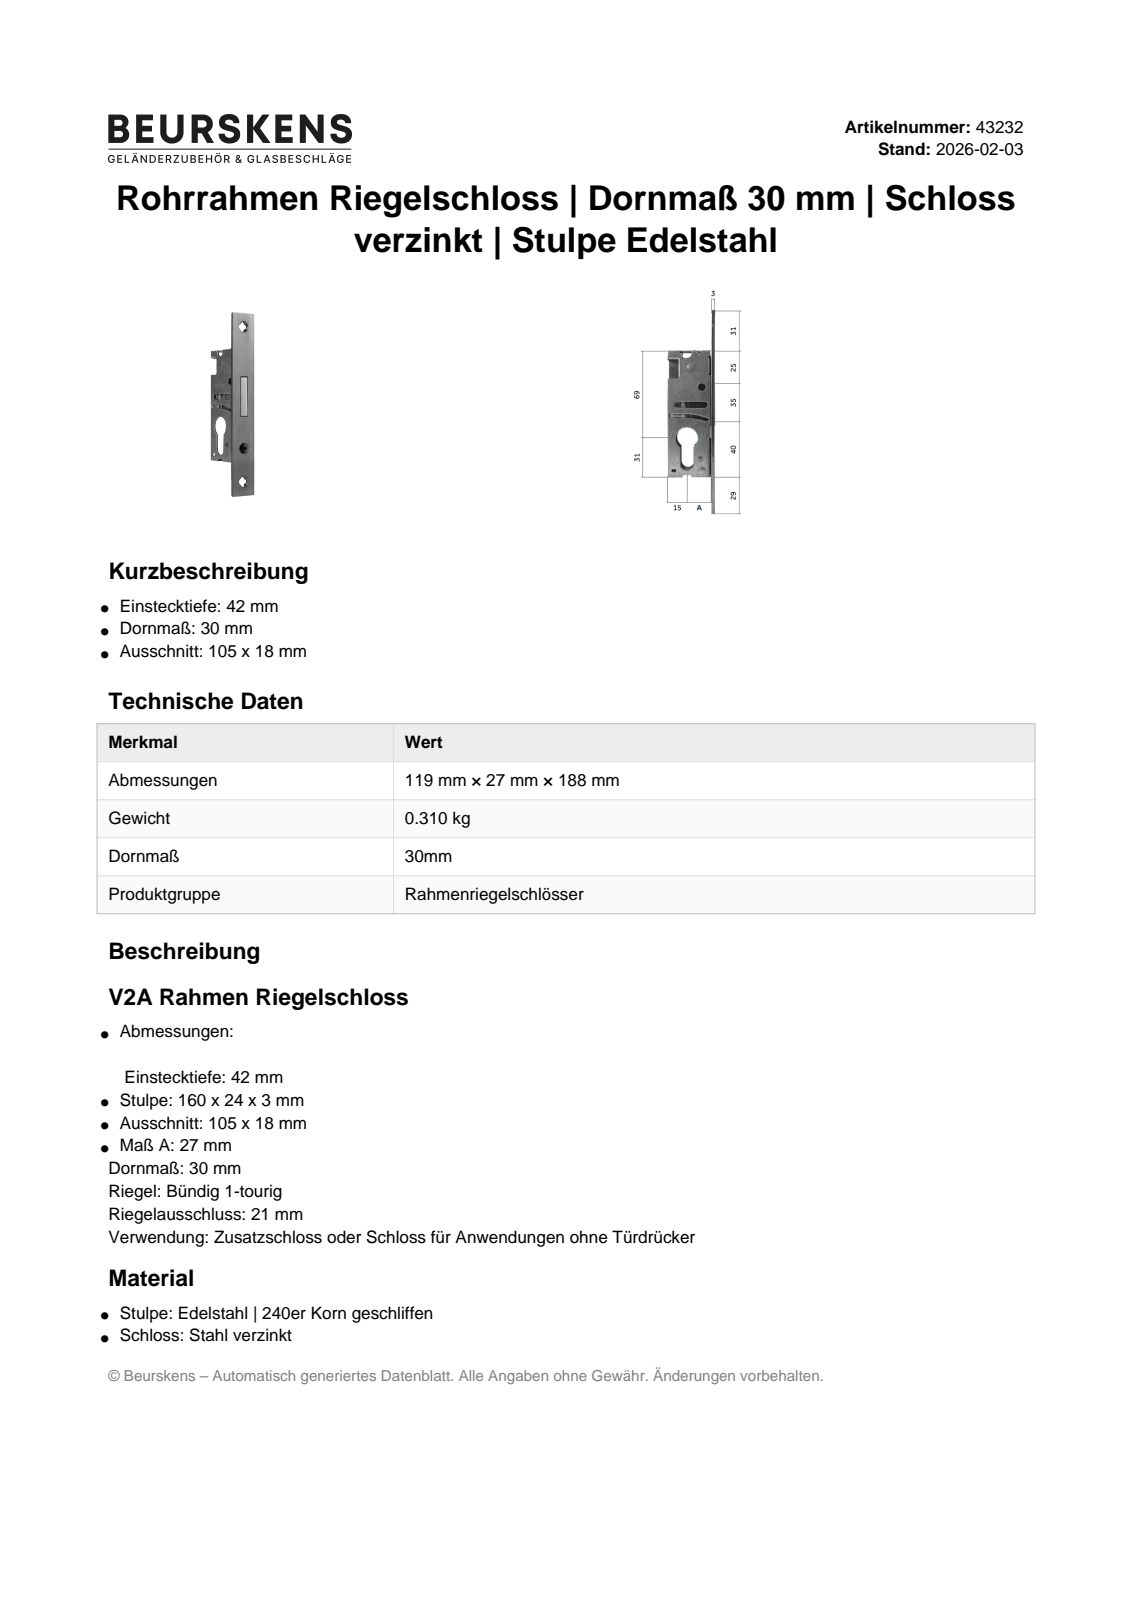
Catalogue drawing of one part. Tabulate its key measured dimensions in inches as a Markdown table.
| quantity | value |
| --- | --- |
| part name | 43232 |
| STEP written by | Autodesk Inventor 2022 (AUTOMOTIVE_DESIGN) |
| units | inches |
| bodies | 1 solid, 26 faces (18 planar, 5 cylindrical, 3 other) |
| overall size | 6.299 × 2.598 × 0.945 |
| volume | 5.234 in³ |
| surface area | 33.48 in² |
| round holes (diameter × count) | 0.197 × 3, 0.689 × 1 |
| partial cylindrical surfaces (radius × count) | 0.207 × 1 |
| main face-to-face distances | 0.709, 0.118, 1.772, 1.654, 0.177, 0.531, 0.827, 0.295, 0.65, 0.945 |
| hole center spacings | 1.407, 3.947, 5.354 |
